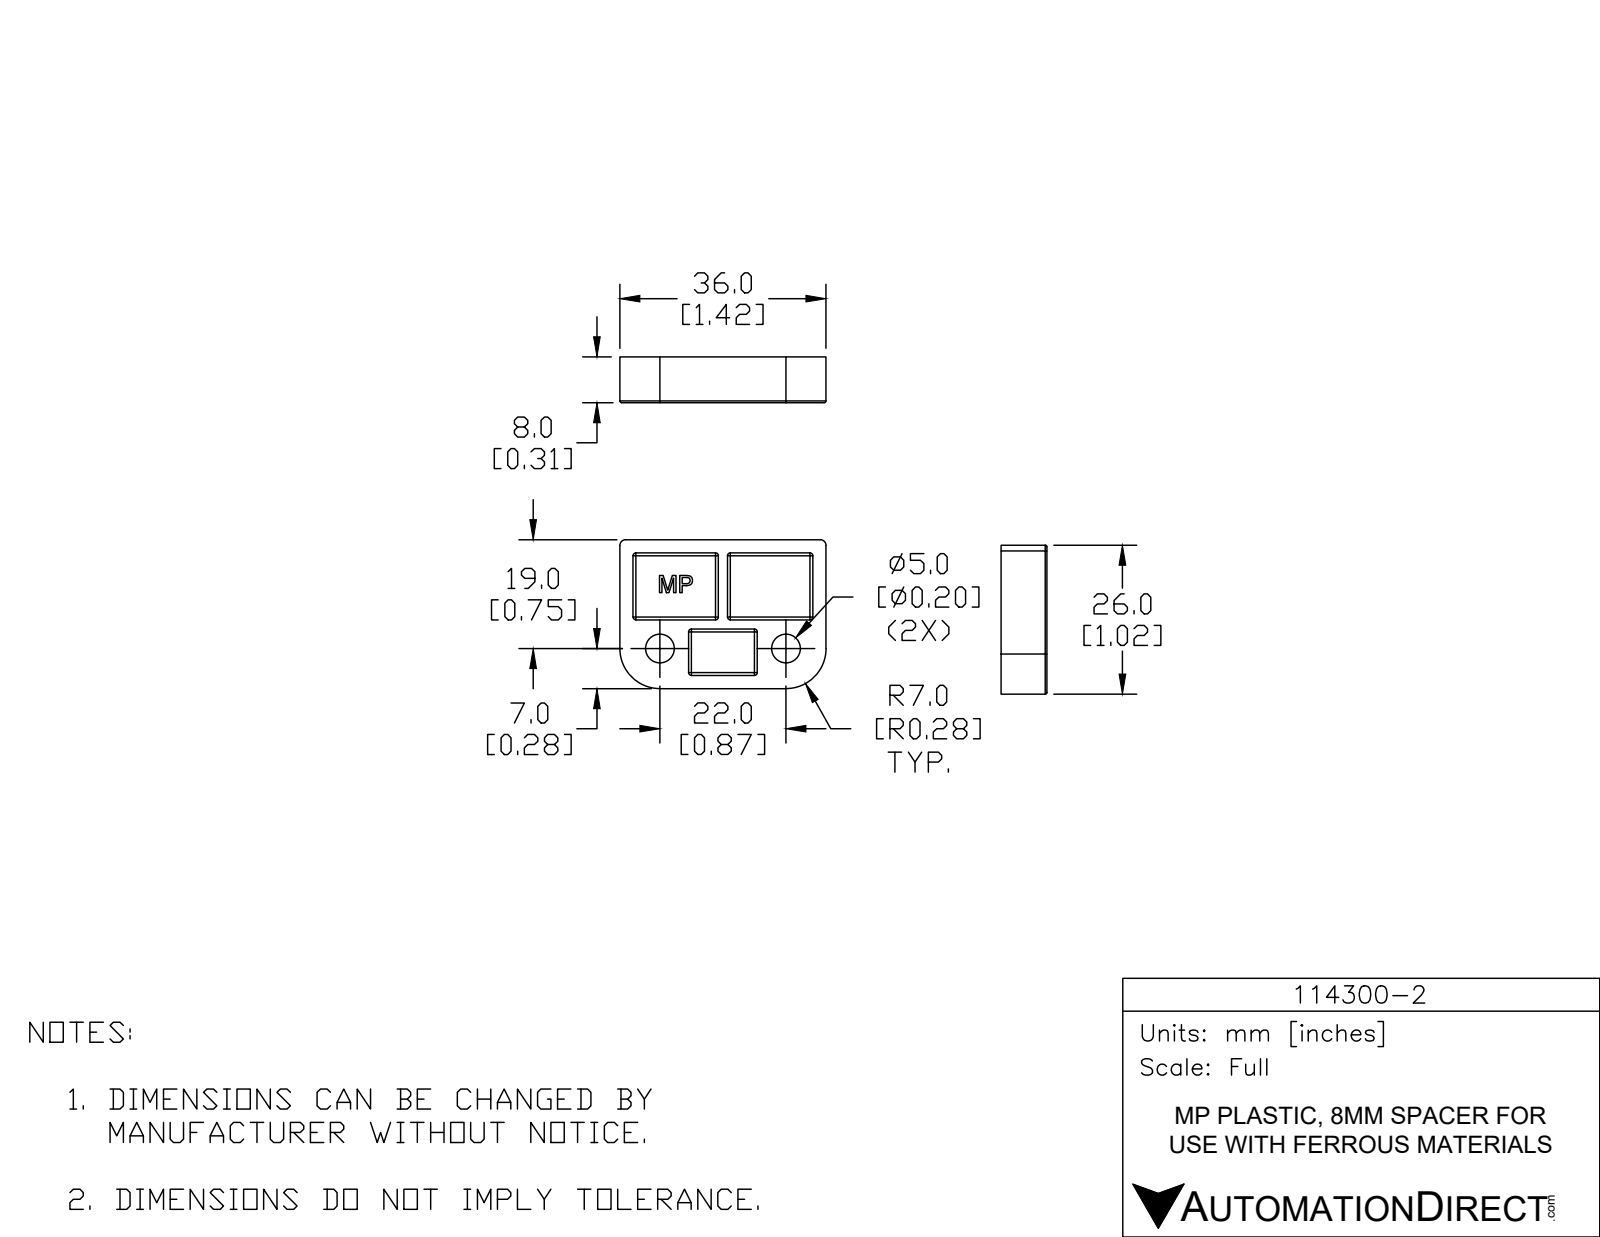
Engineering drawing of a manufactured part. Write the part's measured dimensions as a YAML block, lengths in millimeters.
part_name: "114-MP Spacer"
step_written_by: "SolidWorks 2018 (CONFIG_CONTROL_DESIGN)"
units: millimeters
bodies: {solids: 1, faces: 109, planar: 45, cylindrical: 36, other: 28}
overall_size: [36, 26, 8]
volume: 4761
surface_area: 3608
round_holes:
  - {diameter: 5, count: 2}
partial_cylinders:
  - {radius: 0.5, count: 22}
  - {radius: 0.3, count: 4}
  - {radius: 1, count: 2}
  - {radius: 7, count: 2}
face_to_face_distances: [8, 3, 5, 2.3, 12, 23.7, 26, 36, 14, 11.7]
hole_center_spacings: [22]
